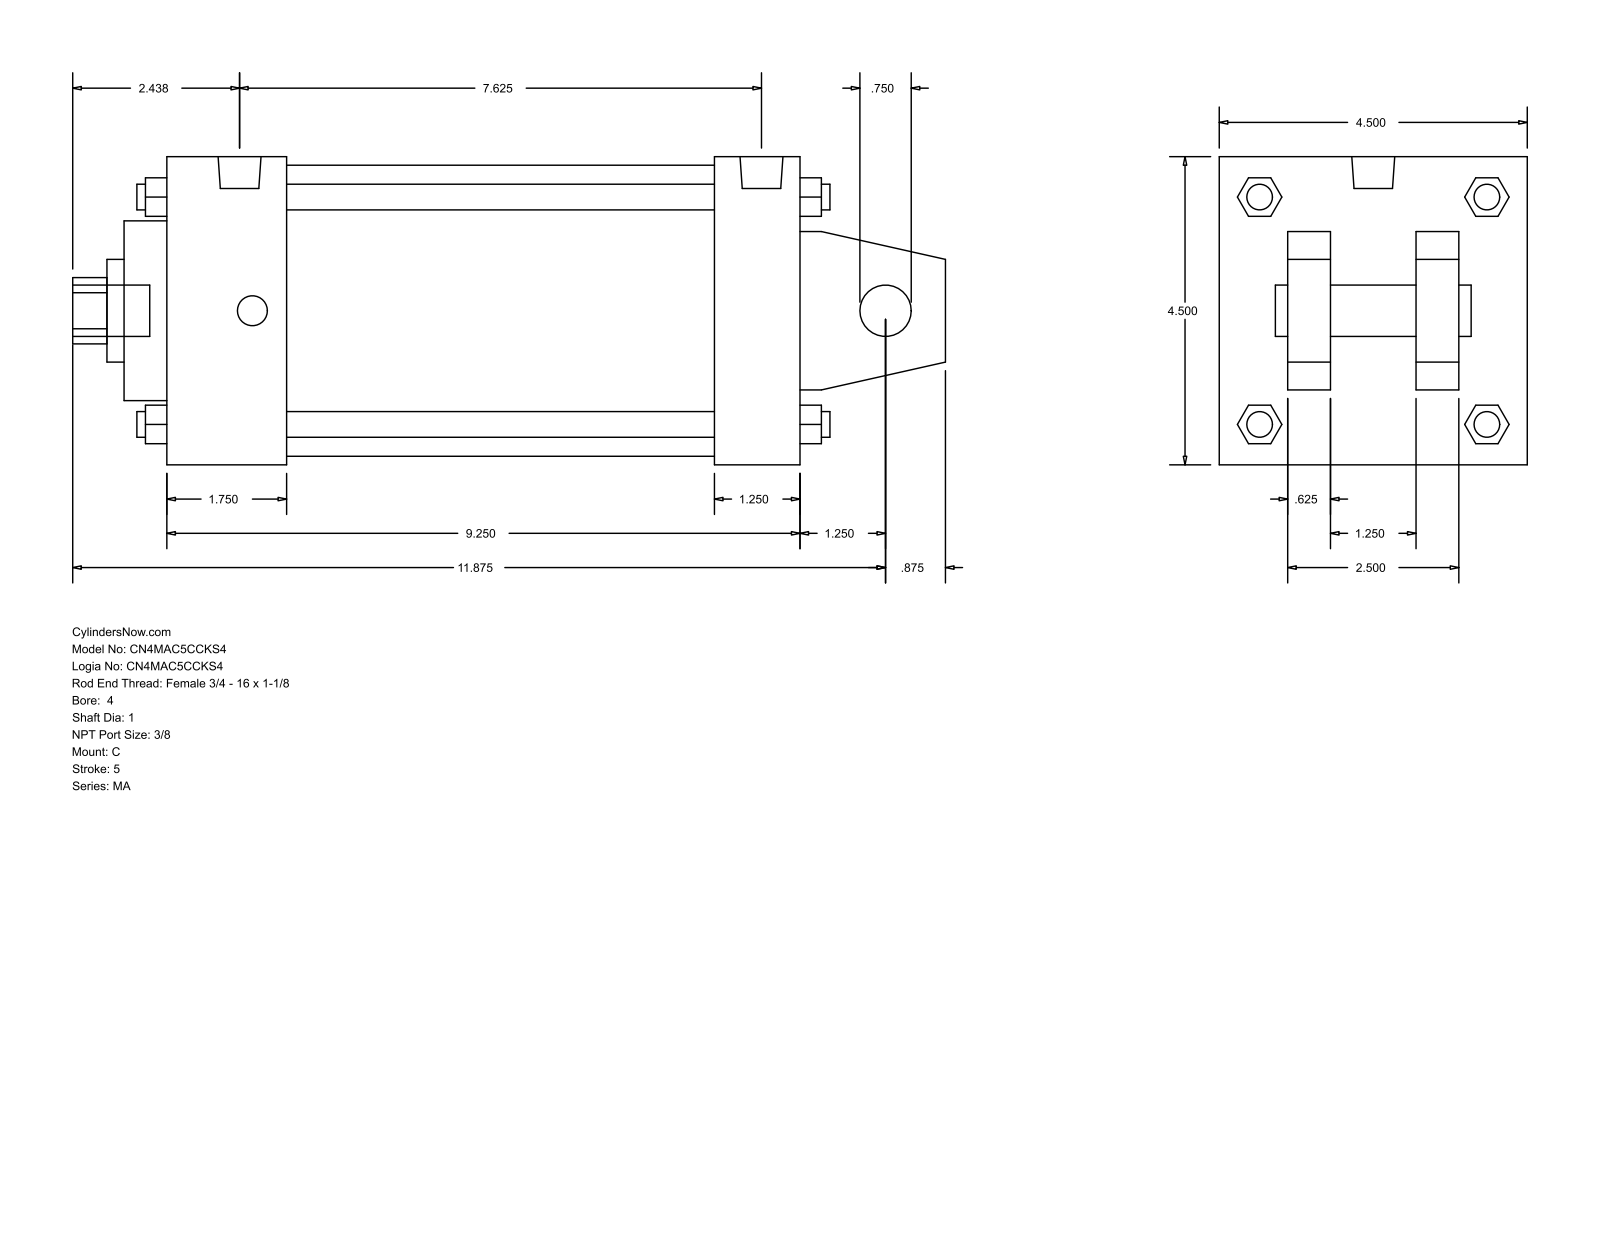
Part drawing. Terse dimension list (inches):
name: MA_C__0400_1
written by: GSSL Pune (CONFIG_CONTROL_DESIGN)
unit: in
bodies: 0 solids, 141 faces (109 planar, 32 cylindrical, 0 other)
size: 12.75 × 4.5 × 4.5
holes: 1× ⌀0.75, 1× ⌀1, 1× ⌀1.5, 1× ⌀2.625, 1× ⌀4.25
bosses: 4× ⌀0.437, 4× ⌀0.375, 2× ⌀0.627, 1× ⌀0.75
rounds: 1× R0.484
face distances: 4.5, 9.25, 0.625, 1.25, 2.875, 1.625, 1, 3.5, 1.875, 8
